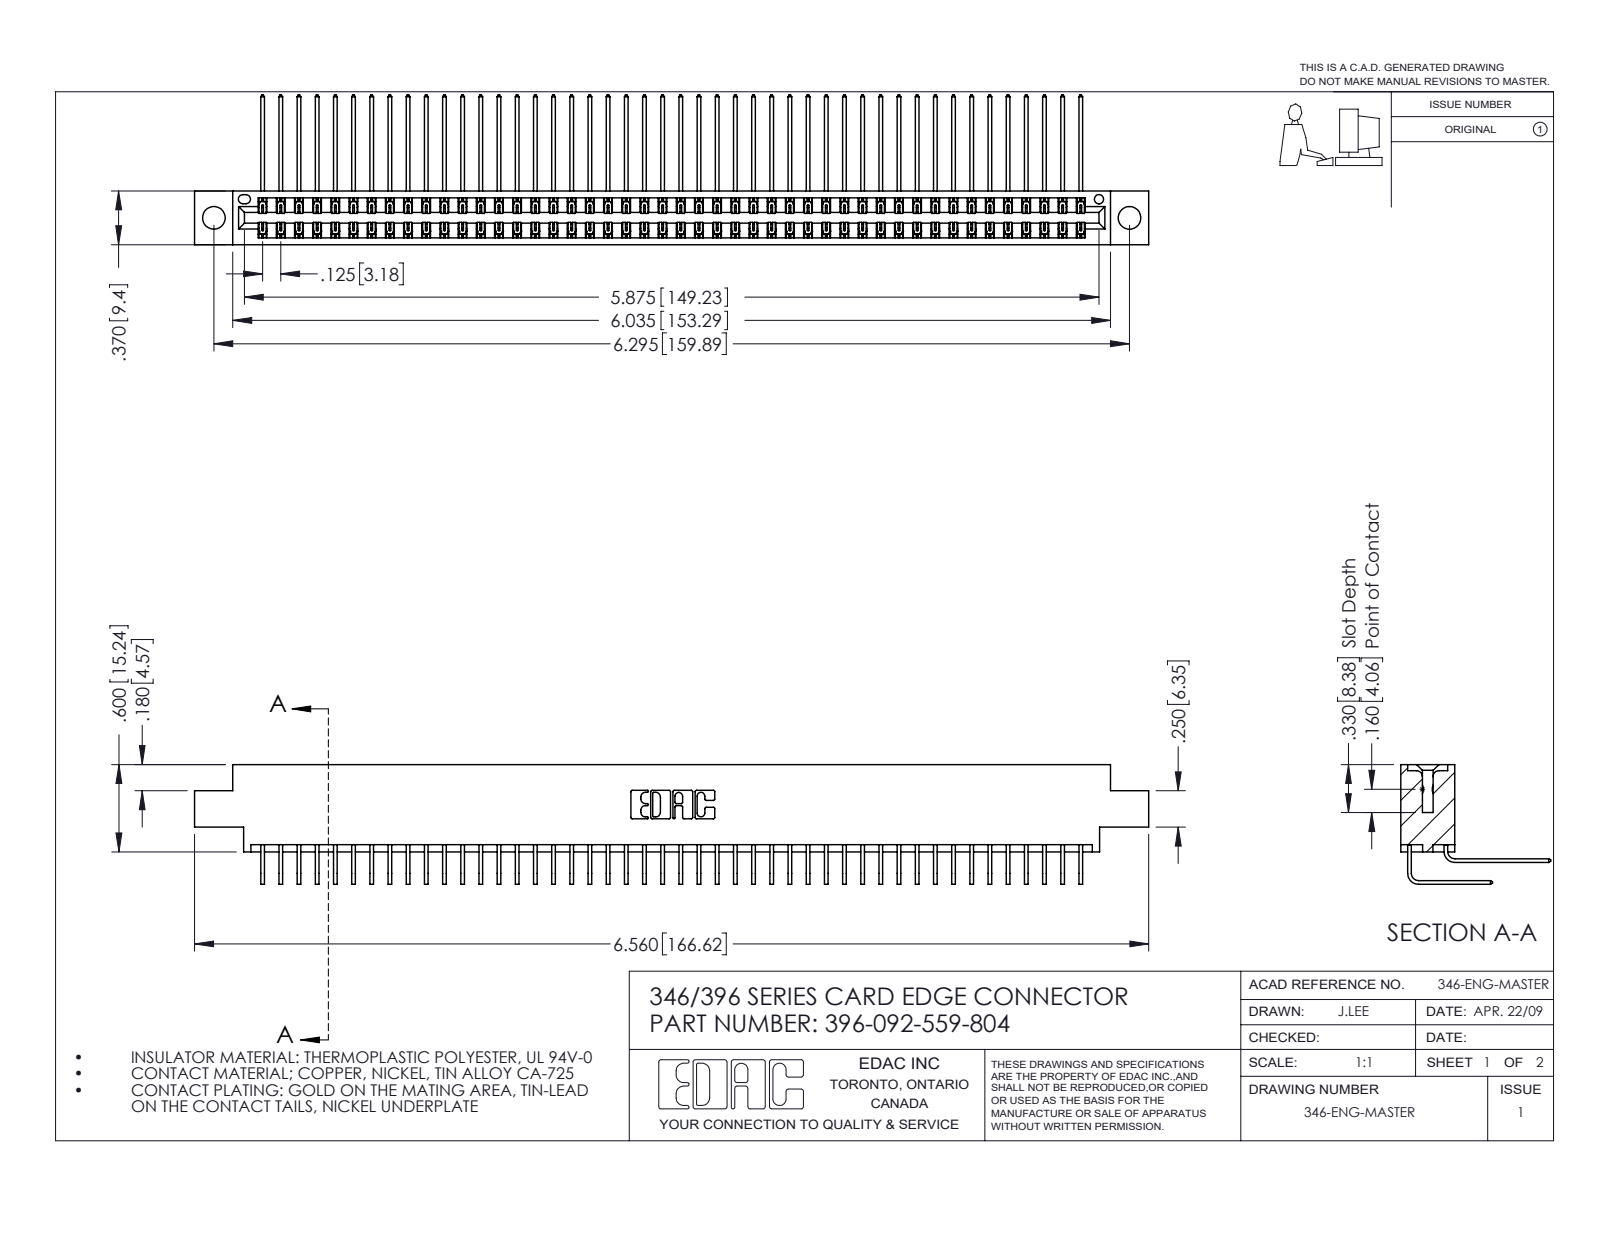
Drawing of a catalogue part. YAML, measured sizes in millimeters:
part_name: "346 Part_0.170 Offset - 0.156 Dia-TH; 396-092-559-804; 345-292-001_559 Tail - 2; 345-292-001_558 559 Tail - 1"
step_written_by: "SolidWorks 2016 (CONFIG_CONTROL_DESIGN)"
units: millimeters
bodies: {solids: 93, faces: 5094, planar: 3484, cylindrical: 1610, other: 0}
overall_size: [166.6, 26.2, 20.9]
volume: 16570
surface_area: 25370
round_holes:
  - {diameter: 4, count: 2}
  - {diameter: 1.6, count: 1}
partial_cylinders:
  - {radius: 0.2, count: 138}
  - {radius: 0.3, count: 22}
  - {radius: 0.2, count: 6}
  - {radius: 0.8, count: 6}
  - {radius: 0.7, count: 3}
  - {radius: 0.4, count: 2}
  - {radius: 0.6, count: 2}
  - {radius: 0.6, count: 2}
face_to_face_distances: [1.2, 8.2, 0.6, 9.4, 6.4, 1.8, 7.6, 7, 3.8, 5.6]
hole_center_spacings: [6.2, 154.6, 159.9]
